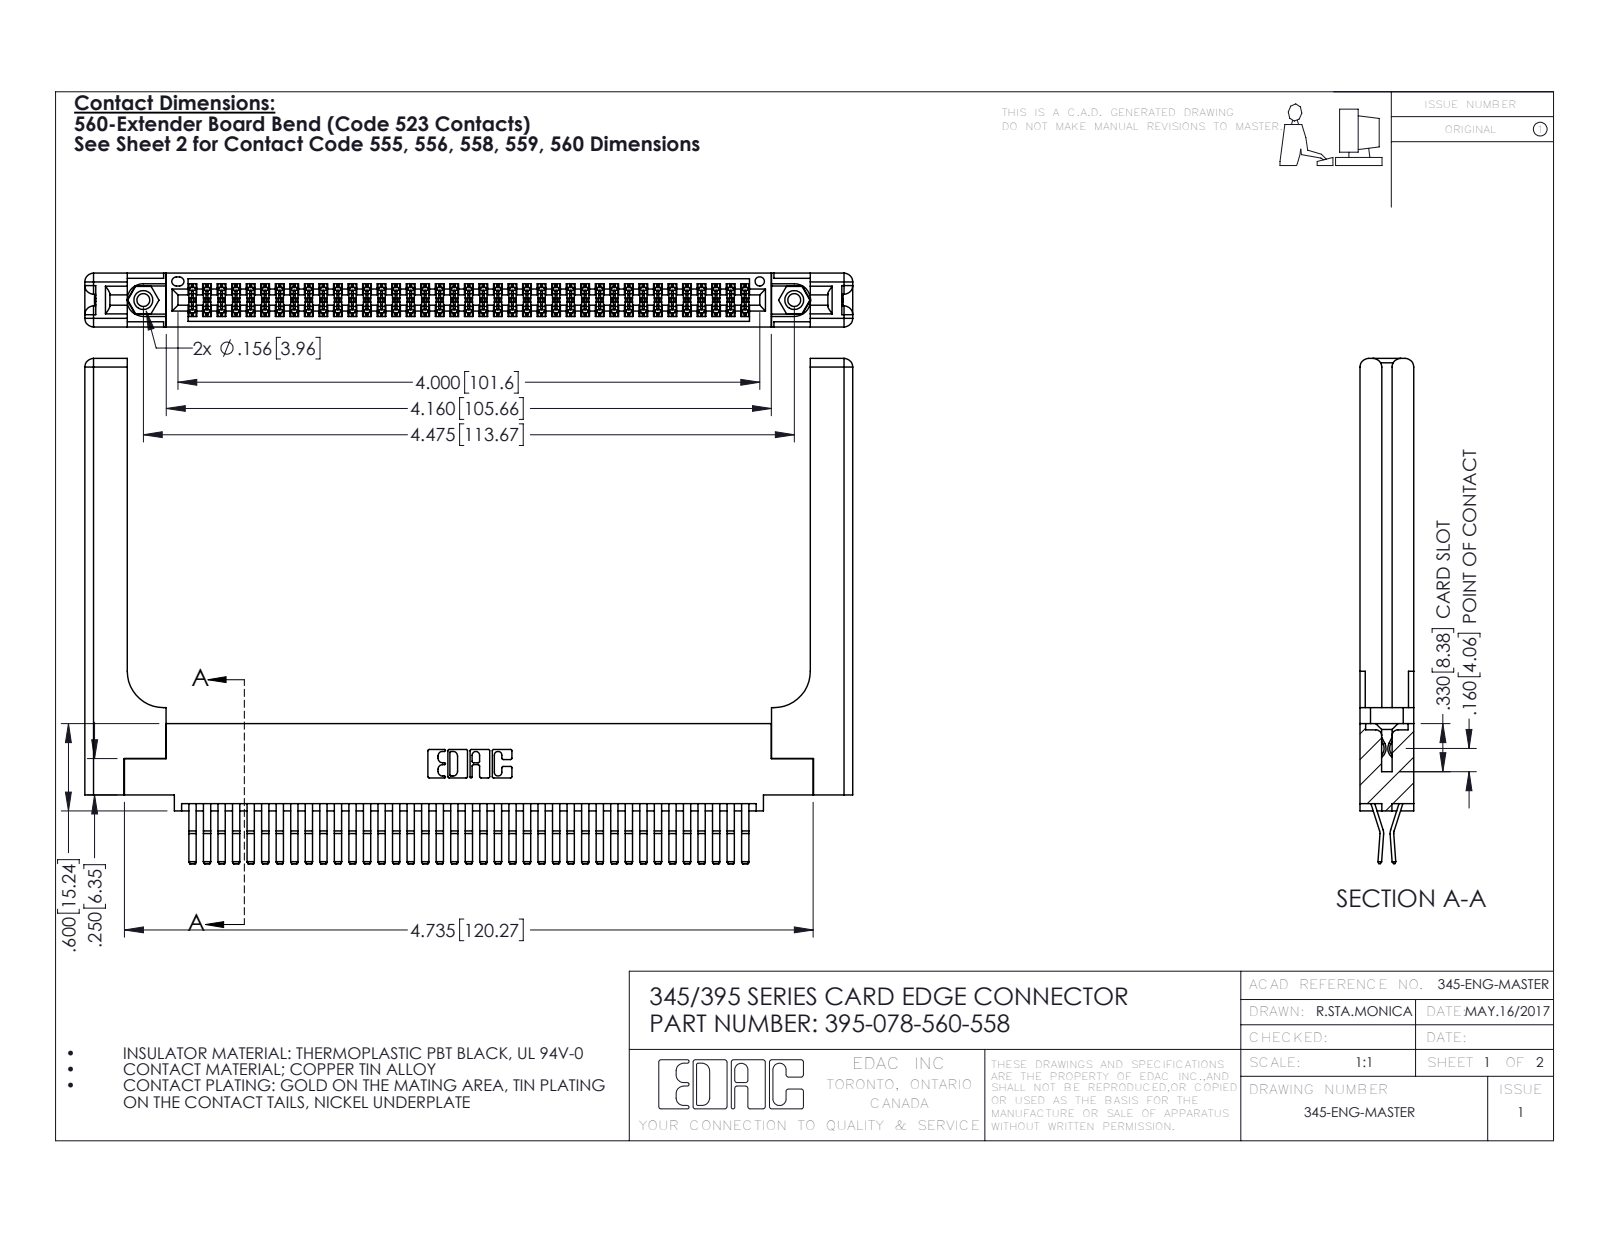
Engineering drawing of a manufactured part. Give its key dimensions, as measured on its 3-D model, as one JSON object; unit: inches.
{"part_name": "395-078-560-558; 345-250-001_345-250-001-102; 345 Part_0.110 Offset - 0.156 Dia-TH; 345-292-001_560 Tail (+1 more)", "step_written_by": "SolidWorks 2016 (CONFIG_CONTROL_DESIGN)", "units": "inches", "bodies": {"solids": 83, "faces": 4442, "planar": 2806, "cylindrical": 1576, "other": 60}, "overall_size": [5.279, 3.472, 0.37], "volume_in3": 1.337, "surface_area_in2": 40.72, "round_holes": [[0.089, 2], [0.125, 2], [0.156, 2], [0.064, 1]], "round_bosses_or_shafts": [[0.155, 2]], "partial_cylinders_radius": [[0.006, 117], [0.01, 22], [0.06, 16], [0.007, 6], [0.031, 6], [0.026, 3], [0.01, 2], [0.014, 2]], "face_to_face_distances": [0.072, 0.37, 0.298, 0.025, 0.2, 0.098, 0.272, 0.225, 0.148, 0.15], "hole_center_spacings": [0.27, 4.239, 4.475]}
